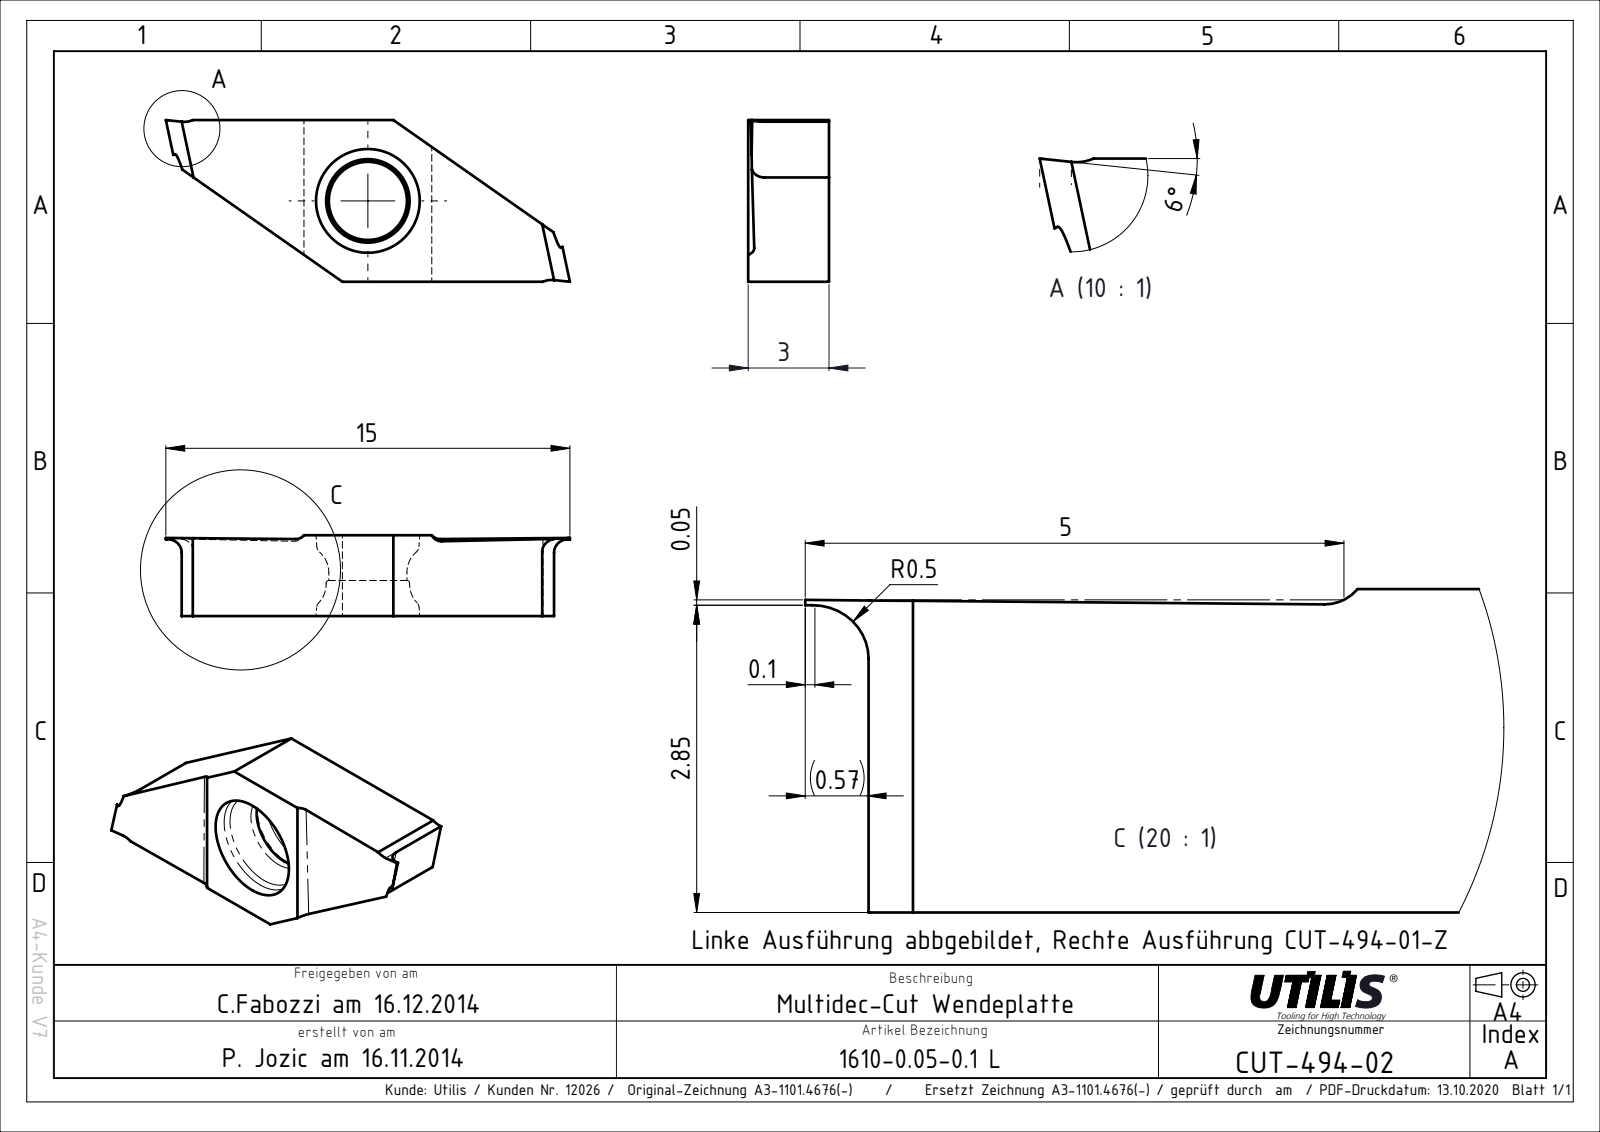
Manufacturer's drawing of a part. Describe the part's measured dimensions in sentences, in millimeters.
The part is named "CUT-494-02". Its 3-D file was written by "SolidWorks 2016 (AUTOMOTIVE_DESIGN)". It is 1 solid with 29 faces: 15 planar, 12 cylindrical and 2 other. Overall it measures 15 by 6 by 3 millimeters. Its volume is 151 cubic millimeters and its surface area 233 square millimeters. Round holes: 1 of diameter 2.9. Partial cylindrical surfaces (rounded edges, fillets, slot ends): 2 of radius 0.4, 2 of radius 0.5. The main face-to-face distances are 6, 6.01, 3, 13.86, 0.57, 14.43, 15, 1.32, 1.68.
